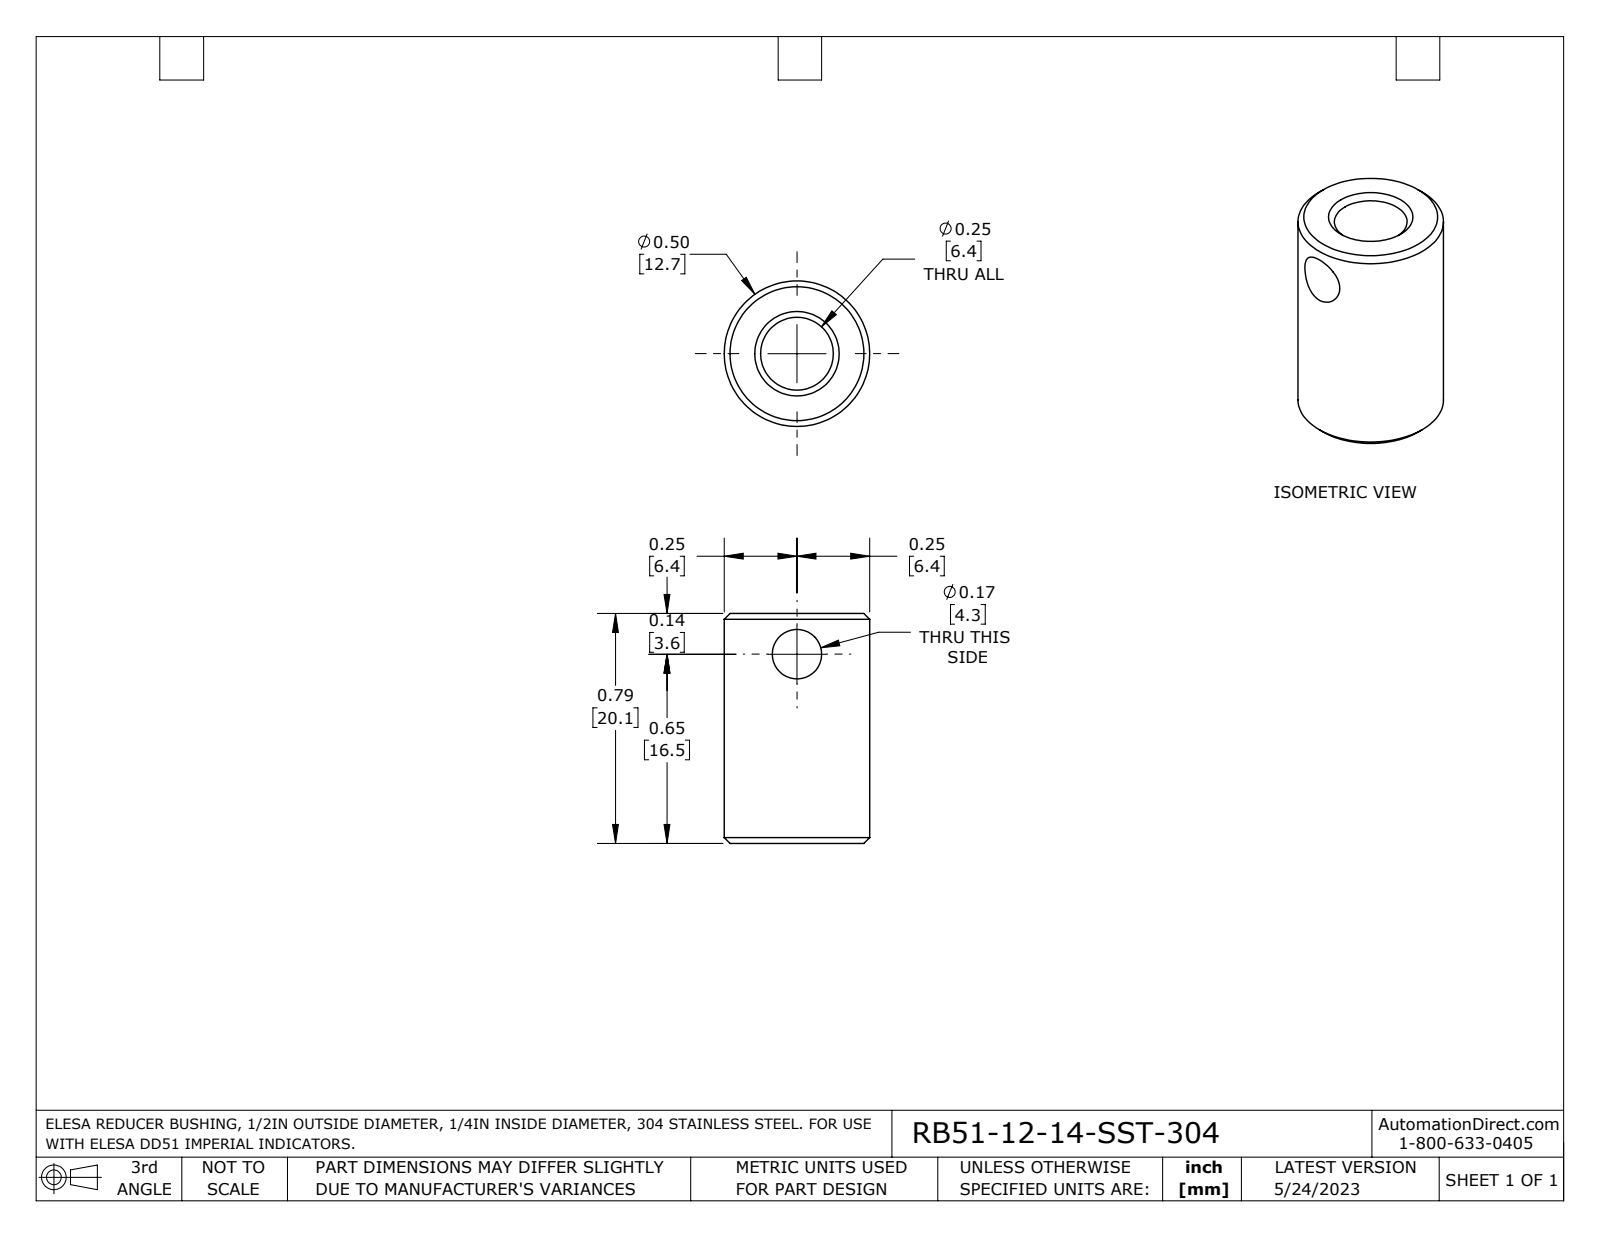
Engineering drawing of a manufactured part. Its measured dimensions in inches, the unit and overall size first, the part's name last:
Units: inches
Overall size (bounding box): 0.79 × 0.5 × 0.5
Round holes (diameter × count): ⌀0.17 ×1, ⌀0.25 ×1
Round bosses / shafts (diameter × count): ⌀0.5 ×1
Main face-to-face distances: 0.79
Volume: 0.112 in³ · Surface area: 2.125 in²
Bodies: 1 solid, 9 faces (2 planar, 3 cylindrical, 4 other)
Part name (STEP PRODUCT): RB51-12-14-SST-304
STEP written by: SolidWorks 2021 (AUTOMOTIVE_DESIGN)
